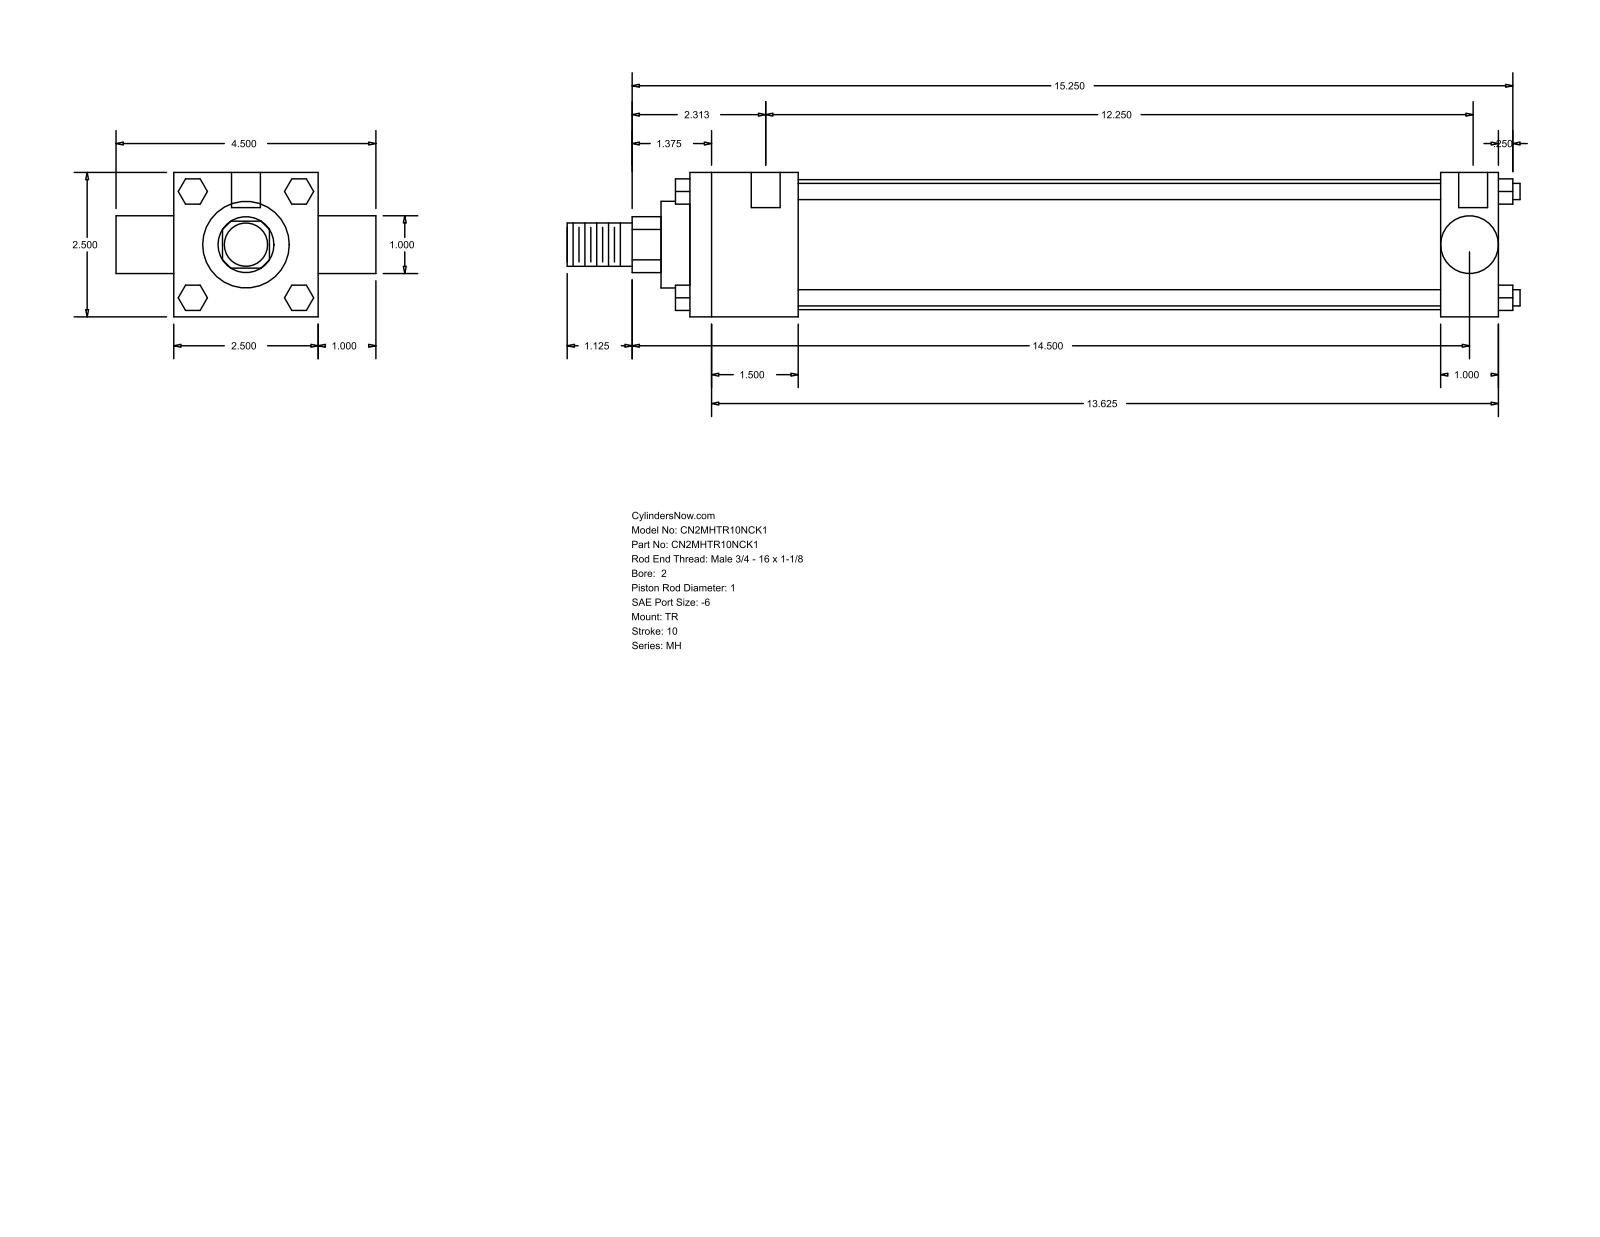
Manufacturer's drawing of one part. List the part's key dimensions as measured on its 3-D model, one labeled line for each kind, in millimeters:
Part name (STEP PRODUCT): MH_TR__0200_1
STEP written by: GSSL Pune (CONFIG_CONTROL_DESIGN)
Units: millimetres
Bodies: 0 solids, 120 faces (92 planar, 28 cylindrical, 0 other)
Overall size (bounding box): 419.1 × 114.3 × 63.5
Round holes (diameter × count): ⌀5.56 ×3, ⌀12.7 ×2
Round bosses / shafts (diameter × count): ⌀7.14 ×4, ⌀57.15 ×1, ⌀38.1 ×1, ⌀25.4 ×1, ⌀25.35 ×1, ⌀19.05 ×1
Partial cylindrical surfaces — rounded edges, fillets, slot ends (radius × count): R12.29 ×1
Main face-to-face distances: 63.5, 355.6, 25.4, 47.63, 330.2, 282.57, 307.97, 88.9, 368.3, 6.35
Hole centre spacings: 3.17, 4.76, 311.15, 314.32, 315.91, 319.08
